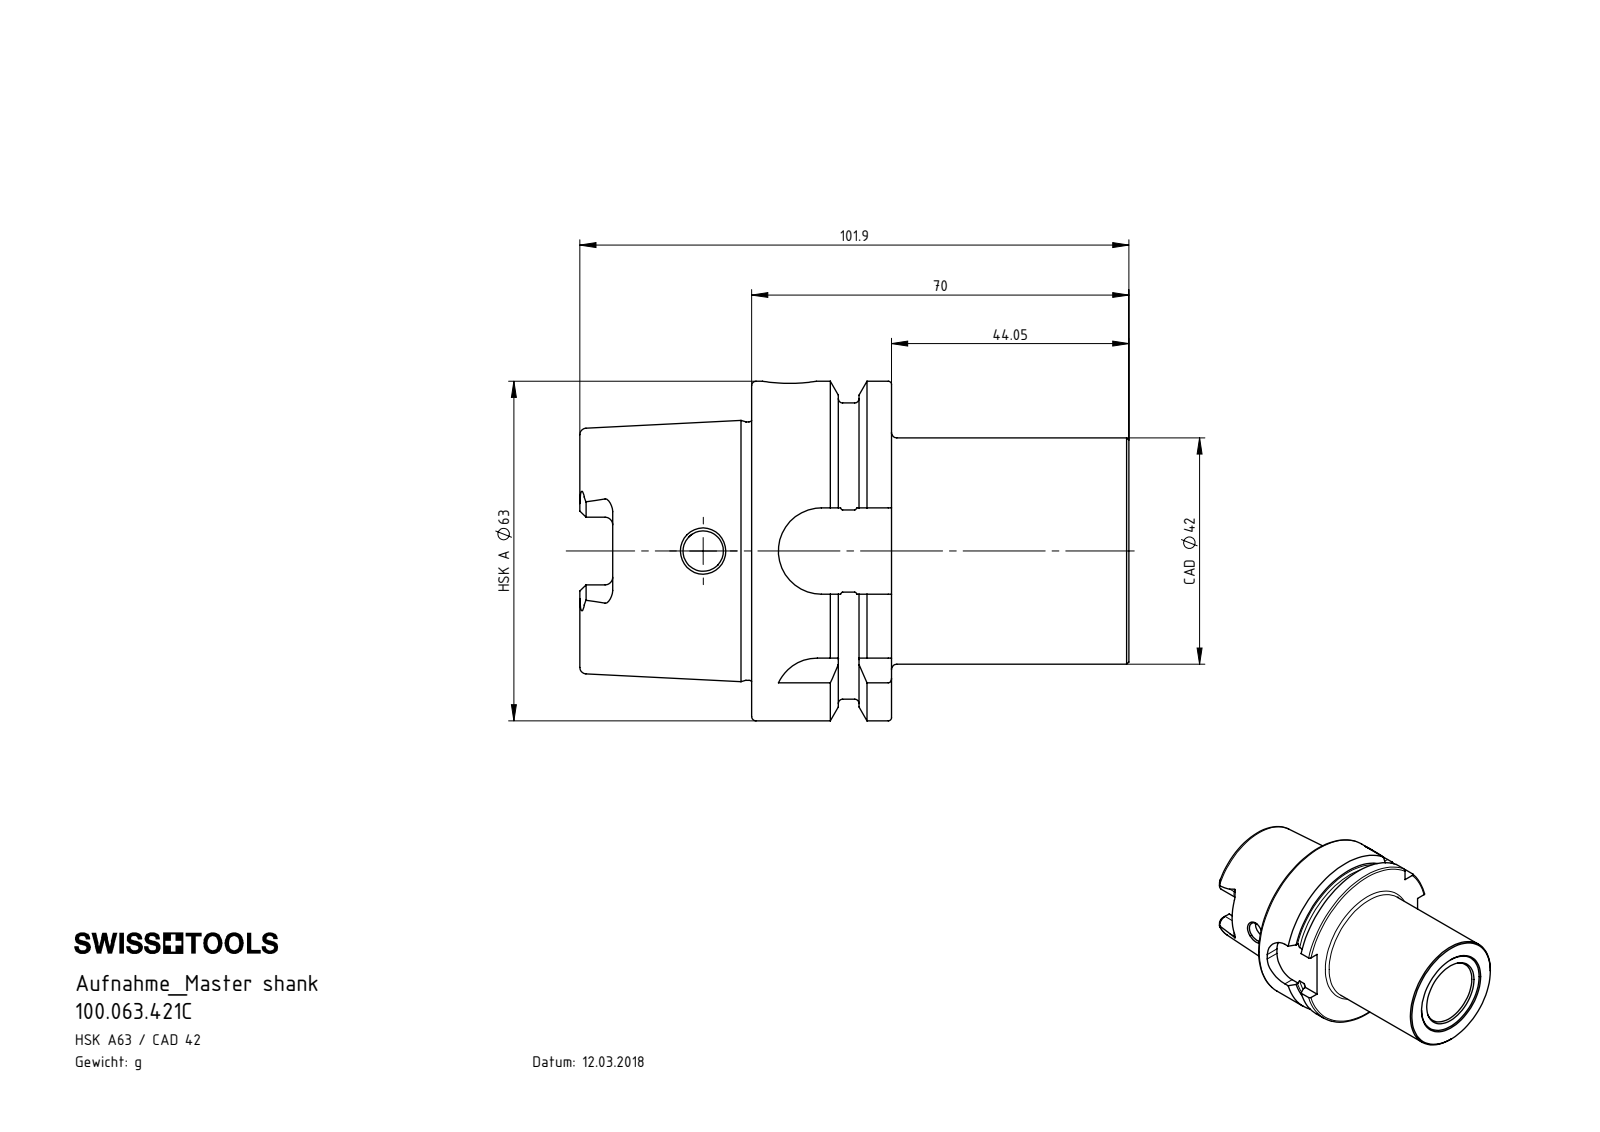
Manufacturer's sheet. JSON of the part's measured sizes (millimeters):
{"part_name": "100.063.421C", "step_written_by": "SolidWorks 2017 (CONFIG_CONTROL_DESIGN)", "units": "millimeters", "bodies": {"solids": 1, "faces": 193, "planar": 49, "cylindrical": 53, "other": 91}, "overall_size": [101.9, 63, 63], "volume_mm3": 124056, "surface_area_mm2": 31164, "round_holes": [[7.5, 1], [8.4, 1], [10, 1], [17, 1], [19, 1], [19.5, 1], [24, 1], [24.45, 1], [24.7, 1], [34, 1], [40, 1]], "round_bosses_or_shafts": [[63, 1], [54.95, 1], [47.94, 1], [42, 1]], "partial_cylinders_radius": [[1.4, 6], [2.88, 4], [8, 4]], "face_to_face_distances": [25.95, 70, 44.05, 16, 9.95, 60.05, 31.9, 41.85, 57.85, 101.9]}
